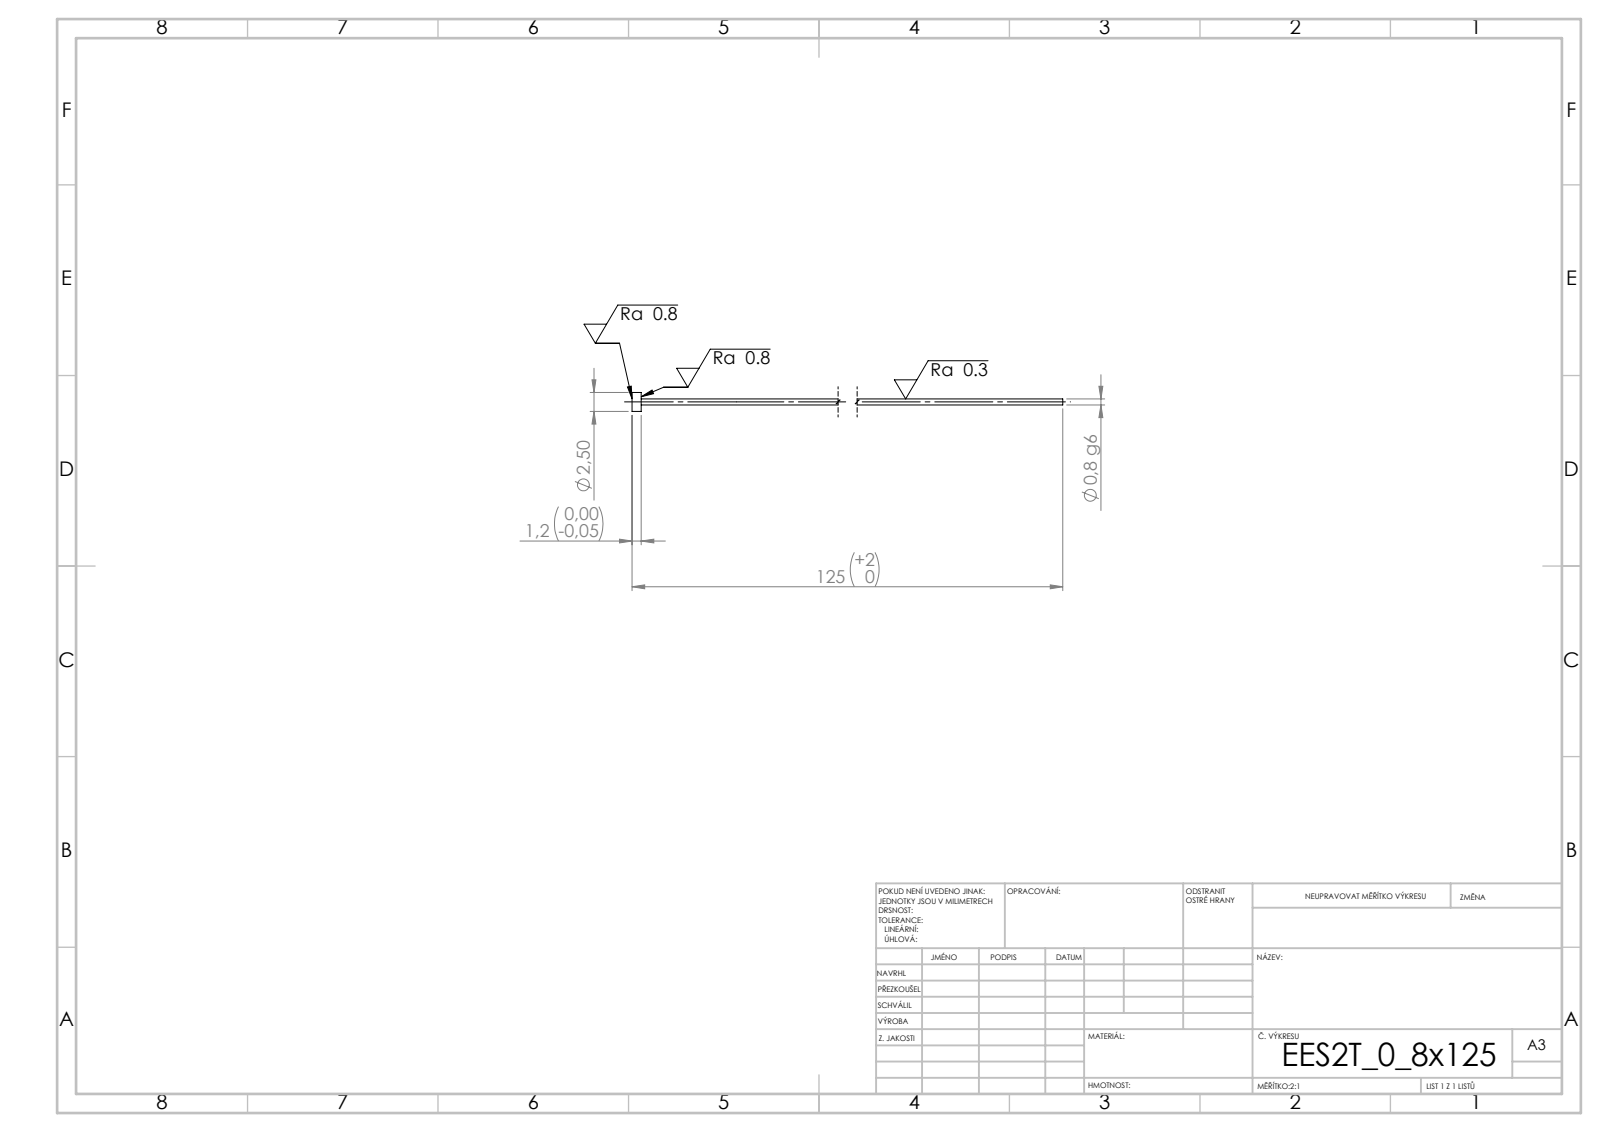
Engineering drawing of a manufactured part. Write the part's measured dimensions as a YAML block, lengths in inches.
step_written_by: "SolidWorks 2019 (CONFIG_CONTROL_DESIGN)"
units: inches
bodies: {solids: 1, faces: 7, planar: 3, cylindrical: 4, other: 0}
overall_size: [4.921, 0.098, 0.098]
volume: 0.004
surface_area: 0.512
round_bosses_or_shafts:
  - {diameter: 0.098, count: 1}
  - {diameter: 0.031, count: 1}
face_to_face_distances: [0.047, 4.921, 4.874]
